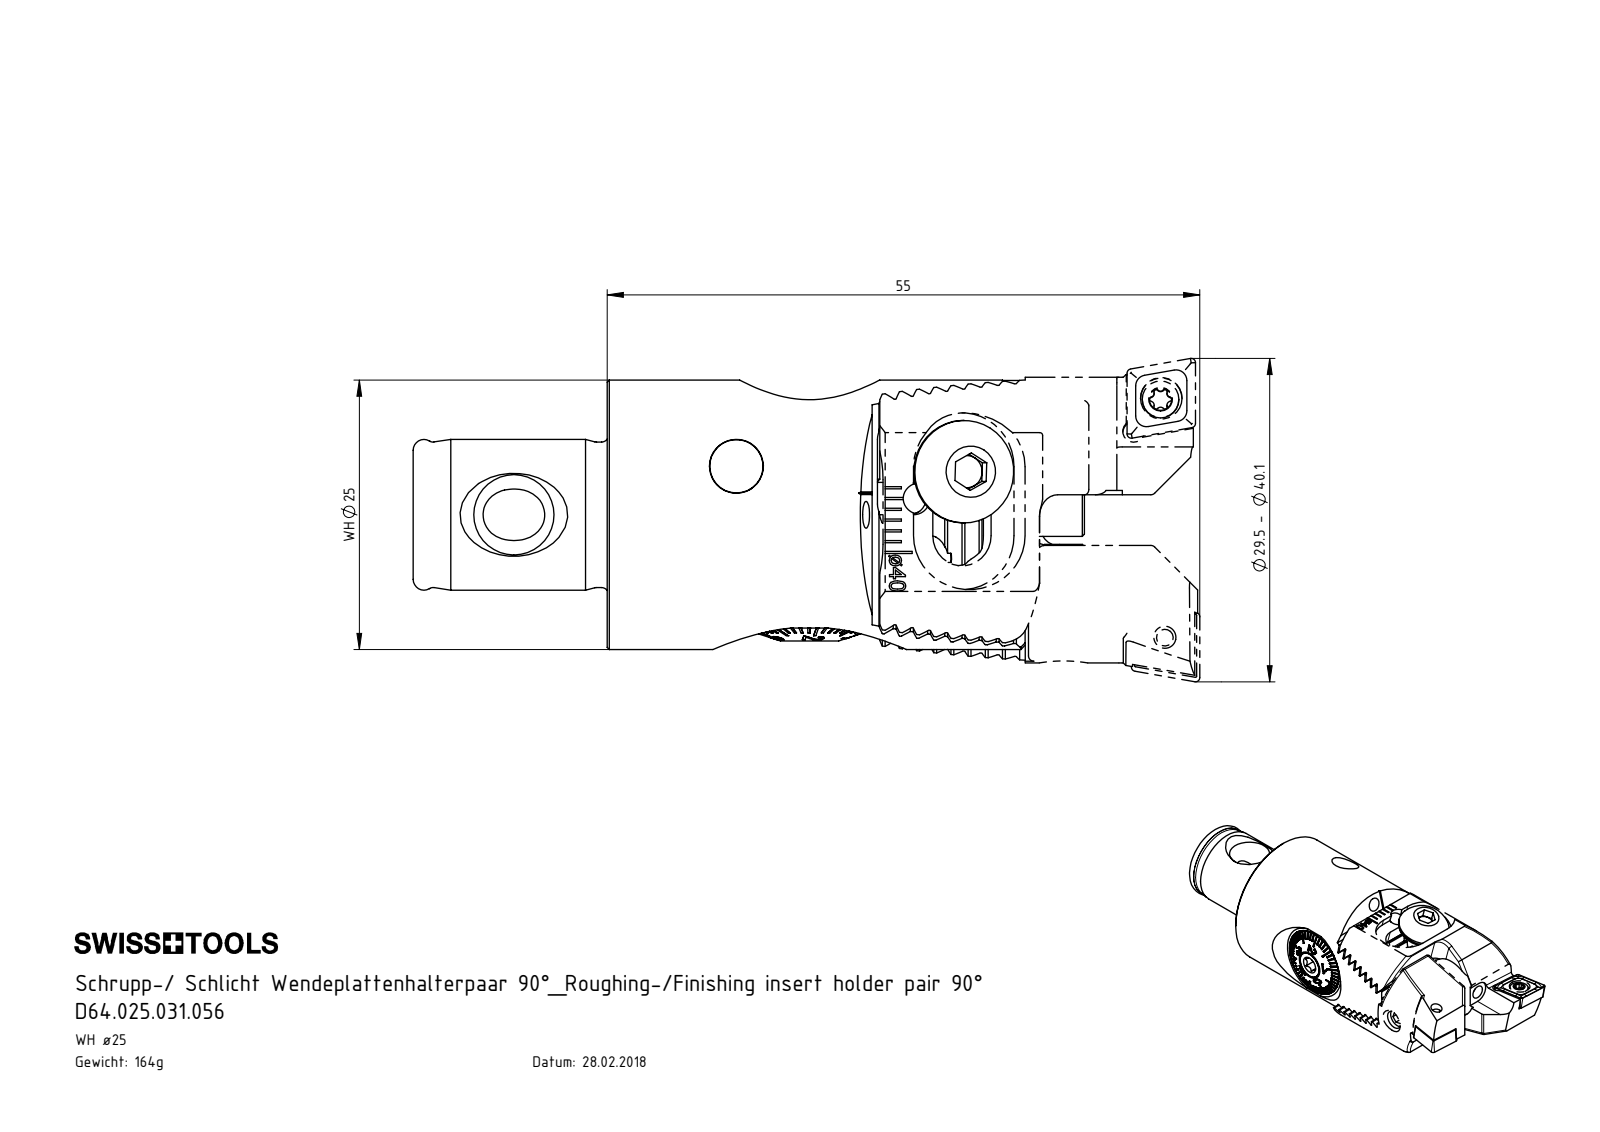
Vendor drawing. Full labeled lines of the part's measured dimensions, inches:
Part name (STEP PRODUCT): ZC2-BG1.013.016; CCMT060204; F25-BG1.009.006_A; WCA-ER2.001.006_A (+8 more)
STEP written by: SolidWorks 2017 (CONFIG_CONTROL_DESIGN)
Units: inches
Bodies: 23 solids, 1466 faces (731 planar, 293 cylindrical, 442 other)
Overall size (bounding box): 2.874 × 1.181 × 0.984
Volume: 1.314 in³ · Surface area: 24.99 in²
Round holes (diameter × count): ⌀0.098 ×4, ⌀0.079 ×3, ⌀0.197 ×3, ⌀0.063 ×2, ⌀0.081 ×2, ⌀0.11 ×2, ⌀0.118 ×2, ⌀0.152 ×2, ⌀0.165 ×2, ⌀0.209 ×2, ⌀0.236 ×2, ⌀0.094 ×1
Round bosses / shafts (diameter × count): ⌀0.118 ×3, ⌀0.374 ×2, ⌀0.362 ×2, ⌀0.197 ×2, ⌀0.195 ×2, ⌀0.157 ×2, ⌀0.134 ×2, ⌀0.098 ×2
Partial cylindrical surfaces — rounded edges, fillets, slot ends (radius × count): R0.02 ×19, R0.005 ×18, R0.005 ×16, R0.008 ×12, R0.014 ×10, R0.079 ×5, R0.11 ×4, R0.197 ×4
Main face-to-face distances: 0.056, 0.113, 0.055, 0.058, 0.169, 0.281, 0.114, 0.225, 0.337, 0.225
Hole centre spacings: 0.154, 0.158, 0.885, 0.165, 0.237, 0.276, 0.646, 0.768
